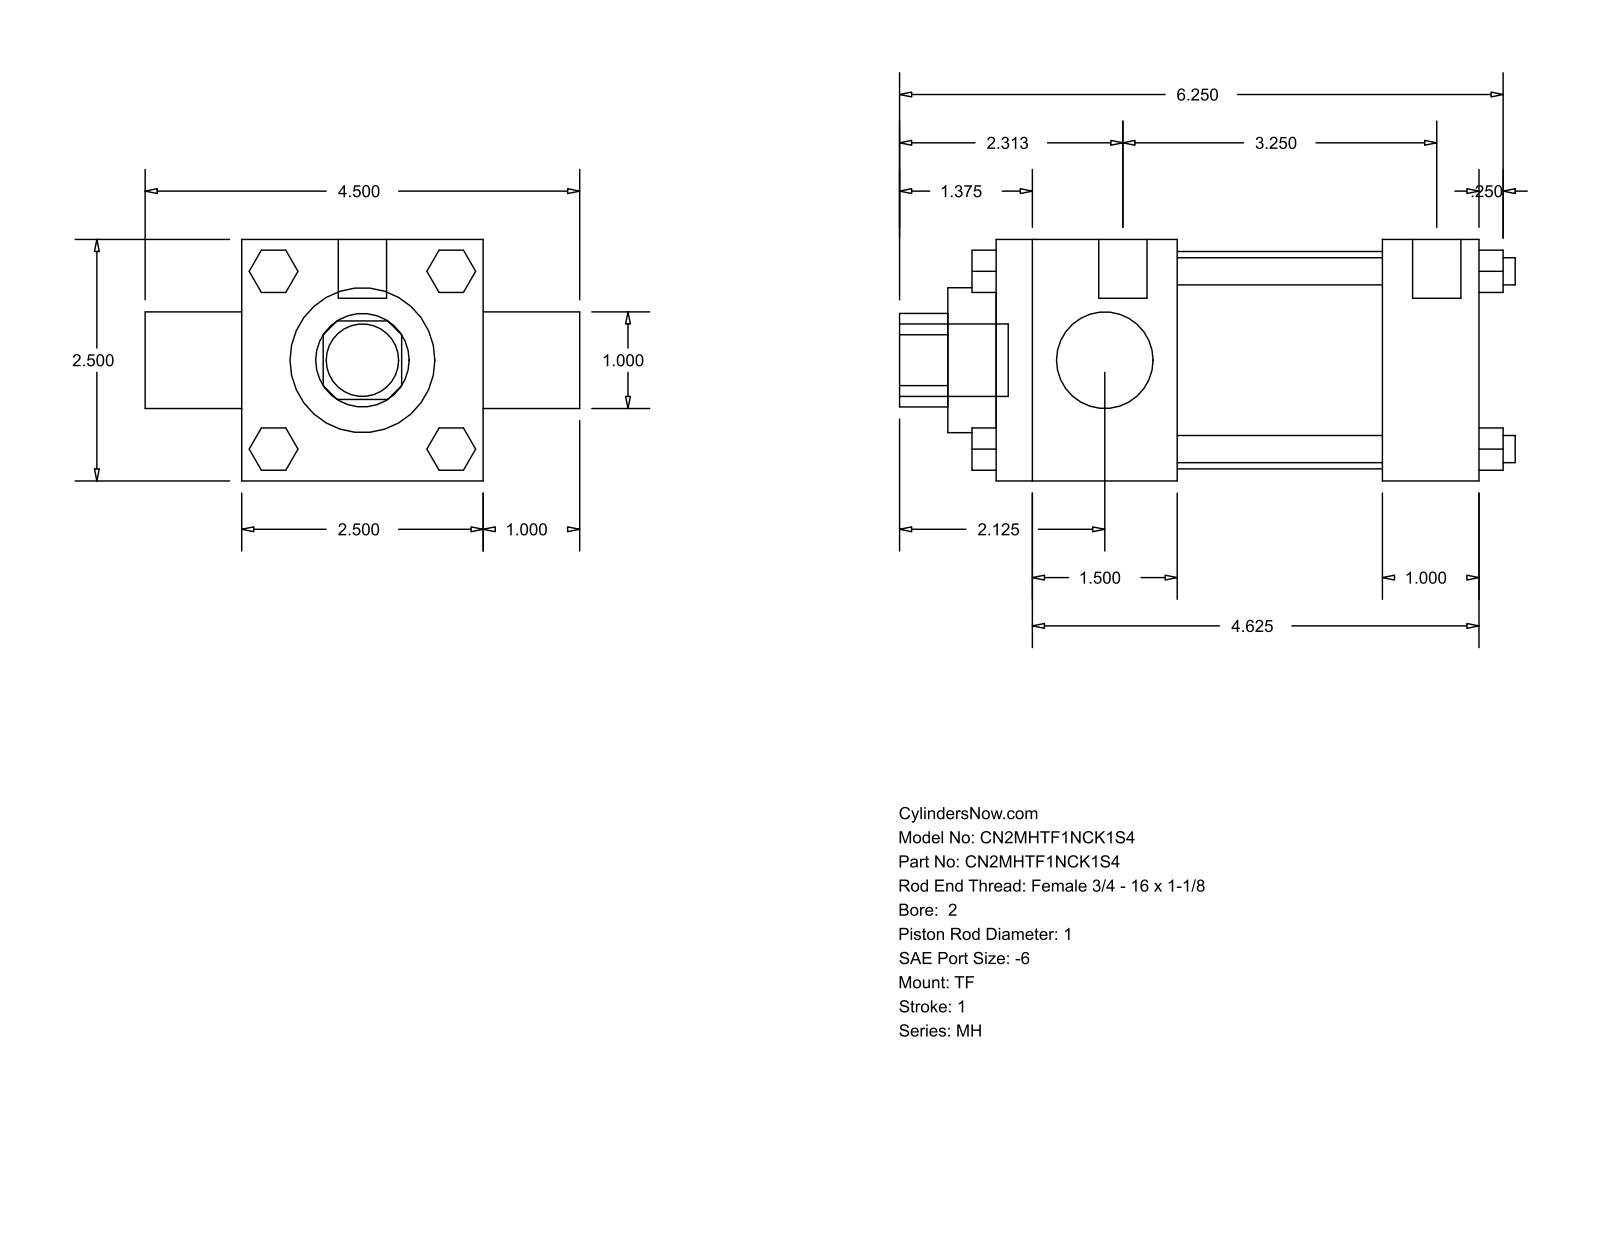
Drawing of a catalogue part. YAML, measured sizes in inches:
part_name: "MH_TF__0200_1"
step_written_by: "GSSL Pune (CONFIG_CONTROL_DESIGN)"
units: inches
bodies: {solids: 0, faces: 120, planar: 92, cylindrical: 28, other: 0}
overall_size: [6.375, 4.5, 2.5]
round_holes:
  - {diameter: 1, count: 2}
  - {diameter: 1.5, count: 1}
  - {diameter: 2.25, count: 1}
round_bosses_or_shafts:
  - {diameter: 0.281, count: 4}
  - {diameter: 0.219, count: 3}
  - {diameter: 0.5, count: 2}
  - {diameter: 0.75, count: 1}
partial_cylinders:
  - {radius: 0.484, count: 1}
face_to_face_distances: [2.5, 5, 1, 1.875, 4, 2.125, 3.125, 3.5, 4.5, 5.5]
